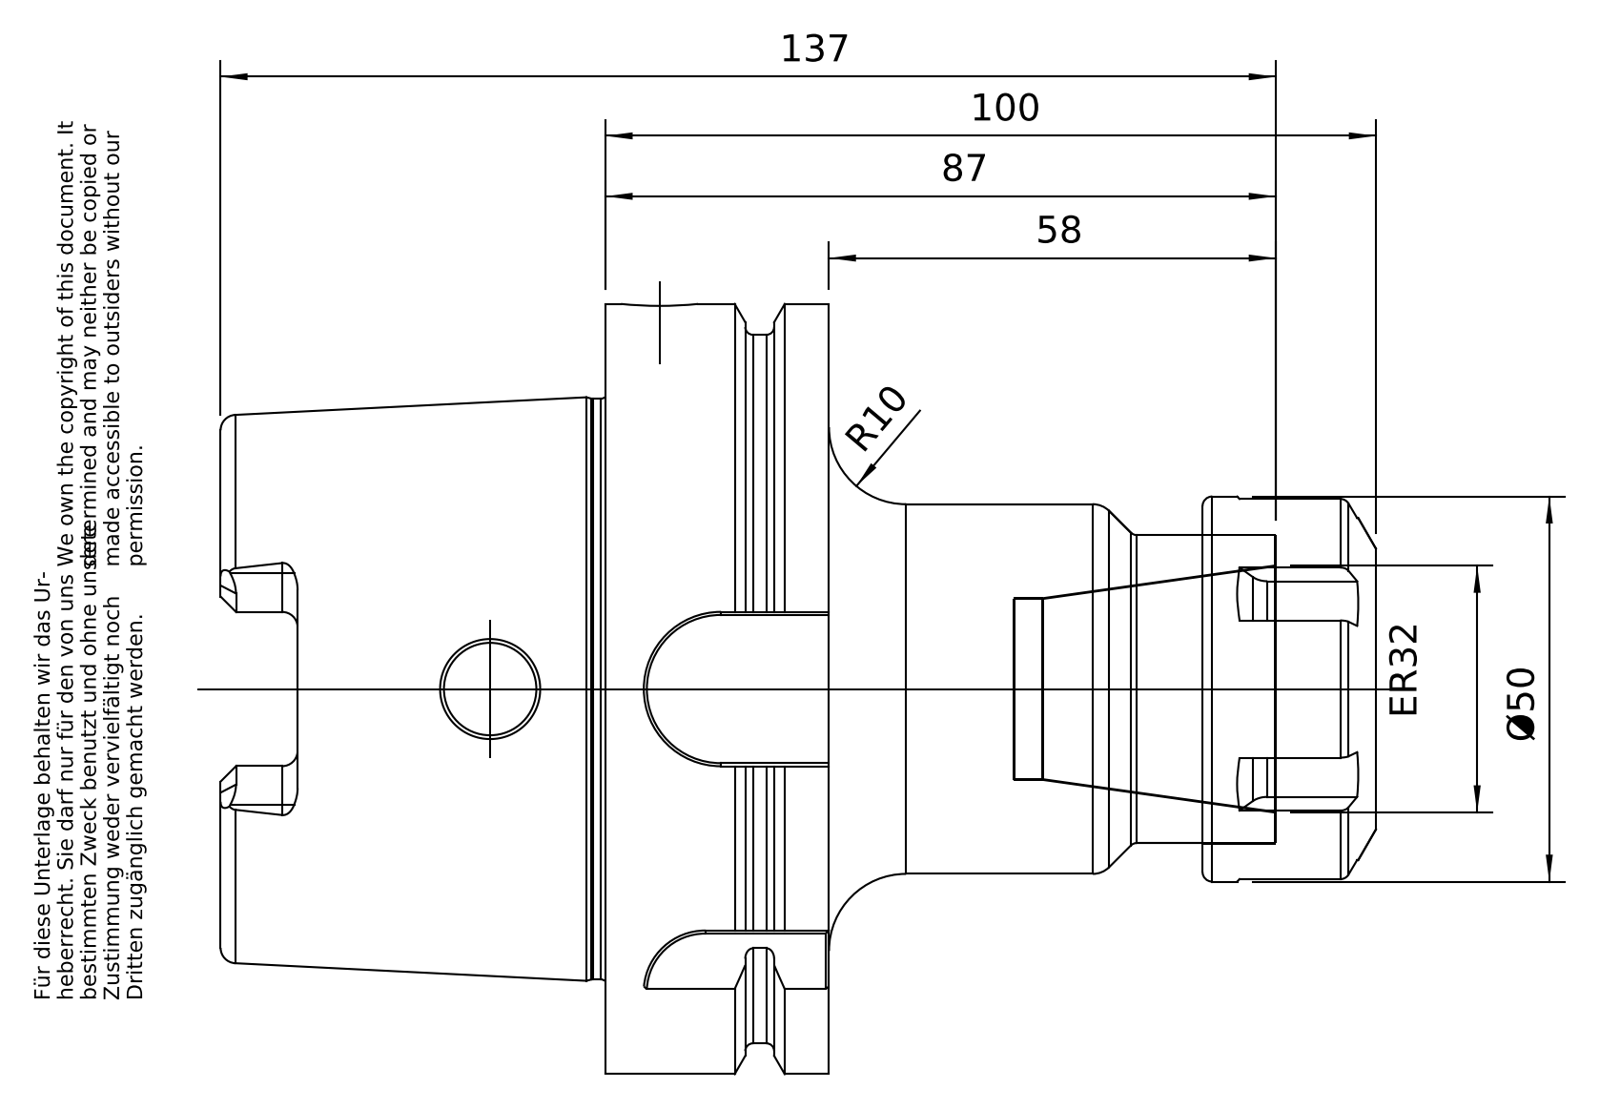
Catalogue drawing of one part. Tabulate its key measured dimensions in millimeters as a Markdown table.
| quantity | value |
| --- | --- |
| part name | A100-020-32; 83-912-32; A100-020-32_ASM |
| STEP written by | PRO/ENGINEER BY PARAMETRIC TECHNOLOGY CORPORATION, 2010430 (CONFIG_CONTROL_DESIGN) |
| units | millimeters |
| bodies | 2 solids, 225 faces (78 planar, 60 cylindrical, 87 other) |
| overall size | 150 × 100 × 100 |
| volume | 371 732 mm³ |
| surface area | 67 324 mm² |
| round holes (diameter × count) | 10 × 1, 12 × 1, 22.5 × 1, 23.5 × 1, 24 × 1, 24.32 × 1, 24.5 × 1, 53 × 1, 63 × 1 |
| round bosses / shafts (diameter × count) | 100 × 1, 92 × 1, 75.36 × 1, 50 × 1, 48 × 1, 40 × 1 |
| partial cylindrical surfaces (radius × count) | 2 × 6, 2.7 × 6, 5 × 4, 8 × 1, 10.02 × 1, 11.02 × 1 |
| main face-to-face distances | 29, 77.5, 48.5, 12.5, 16.5, 65, 100, 87.5, 71, 22.5 |
